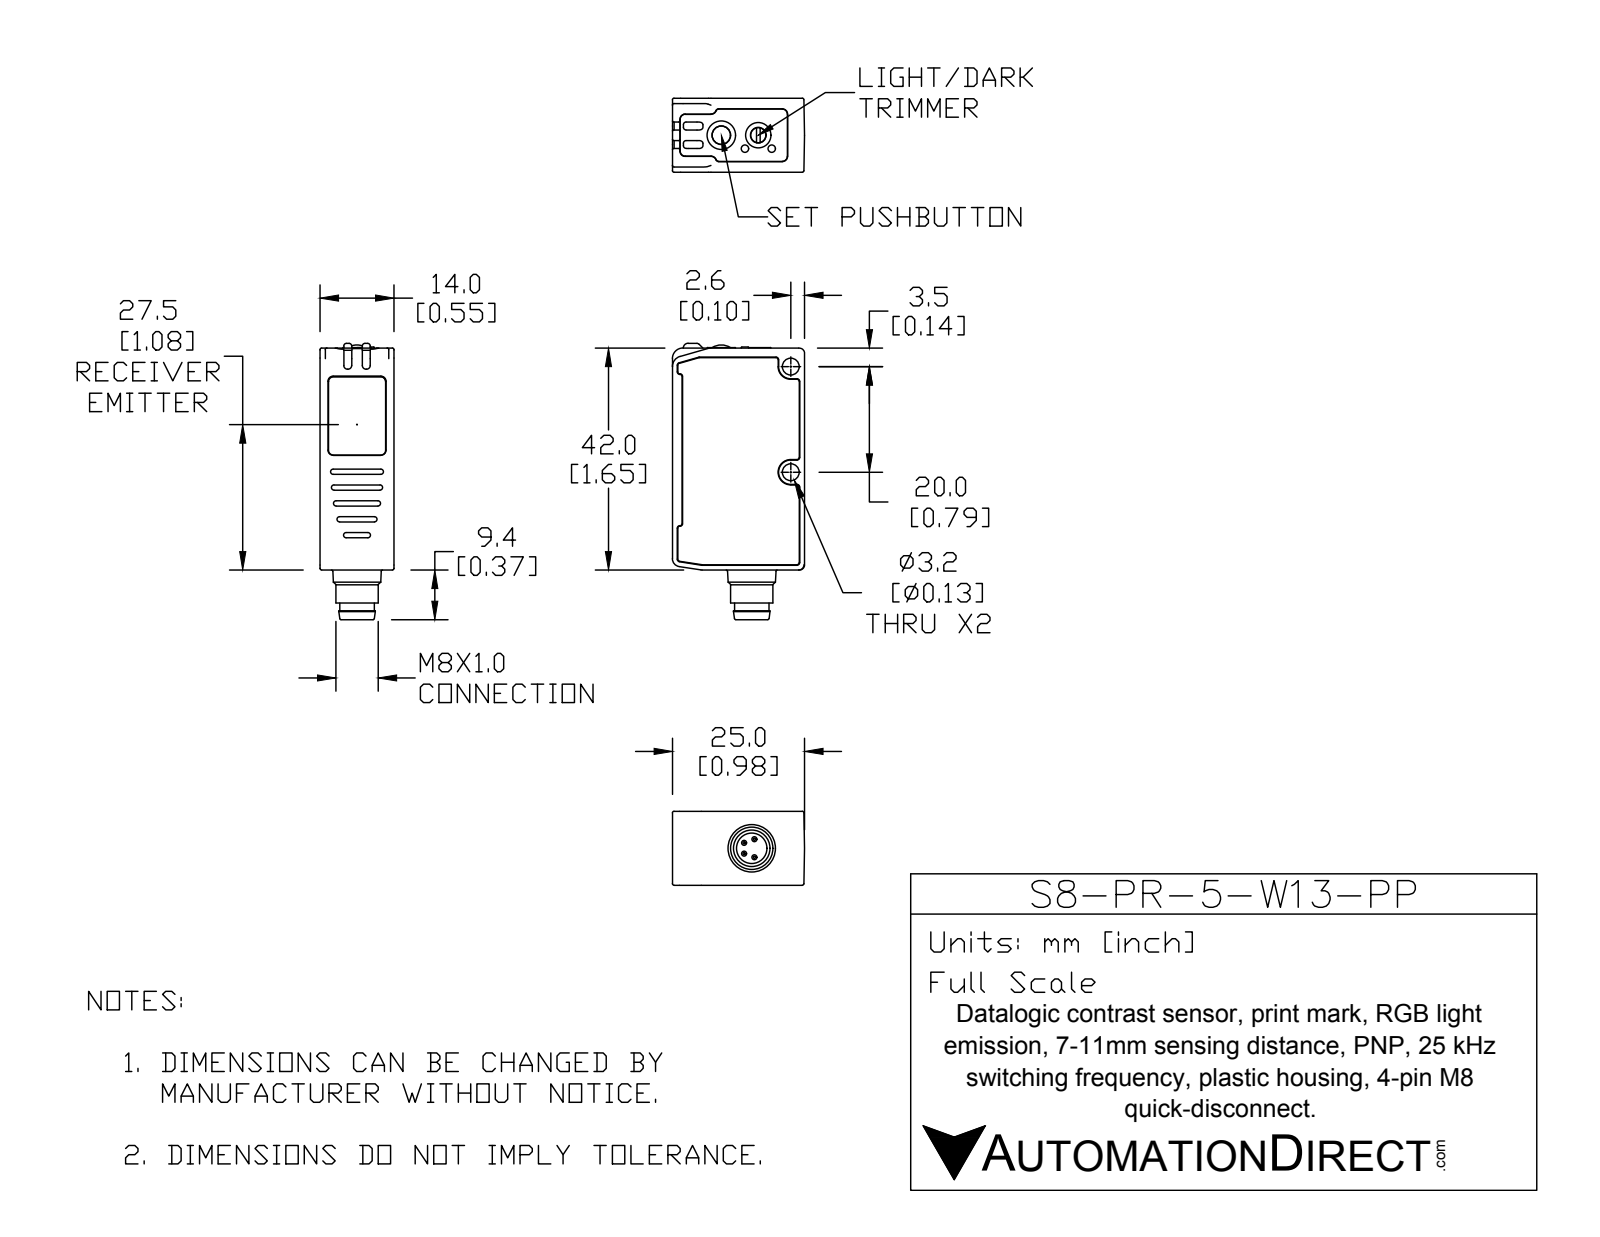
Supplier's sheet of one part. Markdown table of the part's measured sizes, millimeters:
| quantity | value |
| --- | --- |
| part name | S8-PR-5-W13-PP |
| STEP written by | SolidWorks 2016 (AUTOMOTIVE_DESIGN) |
| units | millimeters |
| bodies | 9 solids, 433 faces (126 planar, 191 cylindrical, 116 other) |
| overall size | 52.3 × 25 × 14 |
| volume | 14 595 mm³ |
| surface area | 5 719 mm² |
| round holes (diameter × count) | 3.2 × 2, 1.4 × 1, 2.95 × 1, 3.5 × 1, 5.77 × 1 |
| round bosses / shafts (diameter × count) | 0.95 × 4, 8 × 1, 6.9 × 1, 6.52 × 1, 3.45 × 1, 2.85 × 1, 1.4 × 1 |
| partial cylindrical surfaces (radius × count) | 0.2 × 41, 0.5 × 32, 0.3 × 18, 1 × 14, 0.4 × 13, 0.7 × 4, 0.95 × 4, 2 × 3 |
| main face-to-face distances | 14, 0.6, 0.8, 42, 41.4, 1.8, 22.2, 1, 0.9, 0.5 |
| hole center spacings | 1.25, 3.61, 4.58, 5.75, 7, 9.88, 20 |
